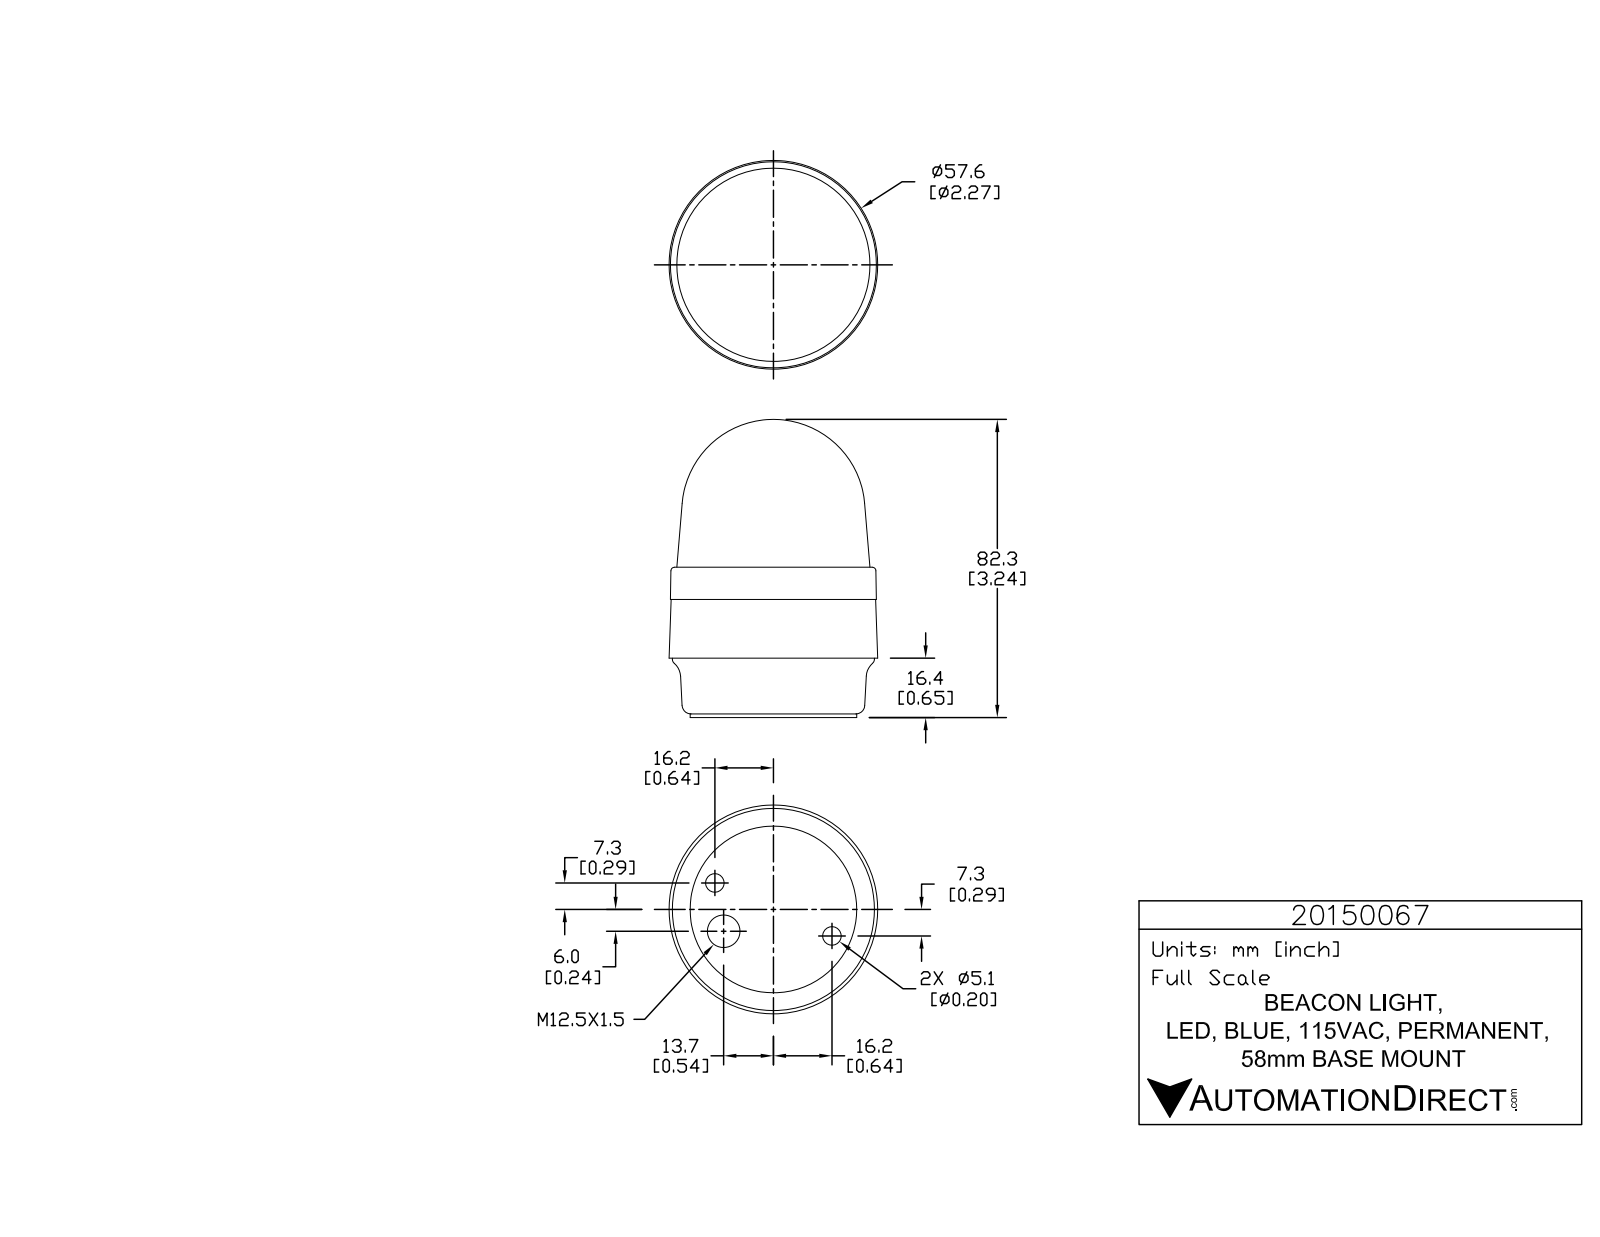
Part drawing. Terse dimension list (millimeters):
name: 20150067
written by: SolidWorks 2015 (AUTOMOTIVE_DESIGN)
unit: mm
bodies: 1 solid, 763 faces (527 planar, 145 cylindrical, 91 other)
size: 82.3 × 57.63 × 57.63
volume: 164 395 mm³; area: 16 261 mm²
holes: 3× ⌀0.99, 2× ⌀5.11, 1× ⌀9
bosses: 3× ⌀5.74, 3× ⌀1.43, 1× ⌀55.8, 1× ⌀46
rounds: 6× R0.2, 6× R0.21, 6× R0.21, 6× R3.32, 3× R0.1, 3× R0.12, 3× R0.19, 3× R0.2
face distances: 16.4, 1, 15.4, 41.5, 40.5, 25.1, 32.6, 31.6, 16.2, 8.9
hole spacings: 13.56, 29.94, 35.5
